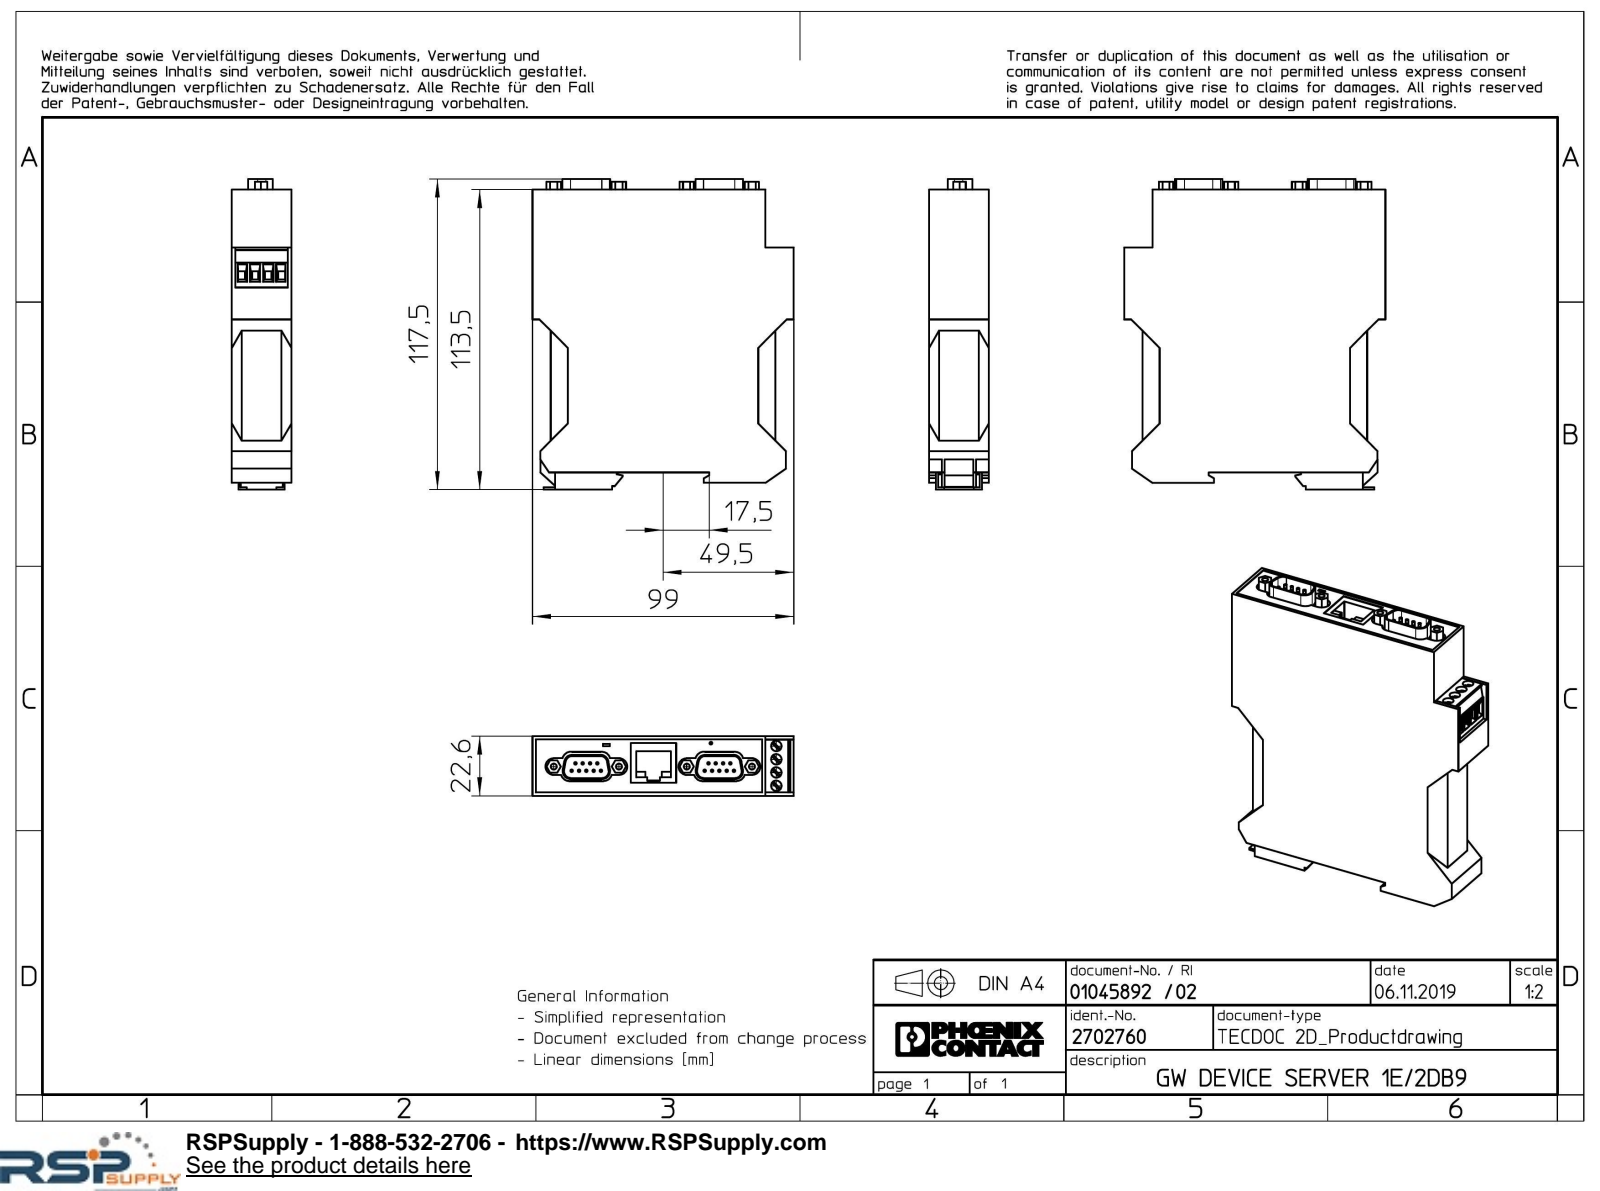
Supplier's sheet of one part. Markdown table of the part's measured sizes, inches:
| quantity | value |
| --- | --- |
| part name | GW...1E_2DB9-select |
| STEP written by | Creo Elements/Direct Modeling 20.1A 29-Sep-2018 (C) Parametric Technology GmbH (AUTOMOTIVE_DESIGN) |
| units | inches |
| bodies | 1 solid, 362 faces (280 planar, 82 cylindrical, 0 other) |
| overall size | 4.626 × 3.898 × 0.89 |
| volume | 13.29 in³ |
| surface area | 50.72 in² |
| round holes (diameter × count) | 0.09 × 4, 0.157 × 4, 0.043 × 1 |
| round bosses / shafts (diameter × count) | 0.039 × 18 |
| partial cylindrical surfaces (radius × count) | 0.125 × 12, 0.1 × 8, 0.12 × 8 |
| main face-to-face distances | 0.89, 0.157, 3.624, 0.274, 4.205, 4.362, 3.35, 0.148, 3.476, 3.203 |
| hole center spacings | 0.197, 0.394, 0.974, 1.984, 0.373, 0.378, 0.462, 0.473 |
